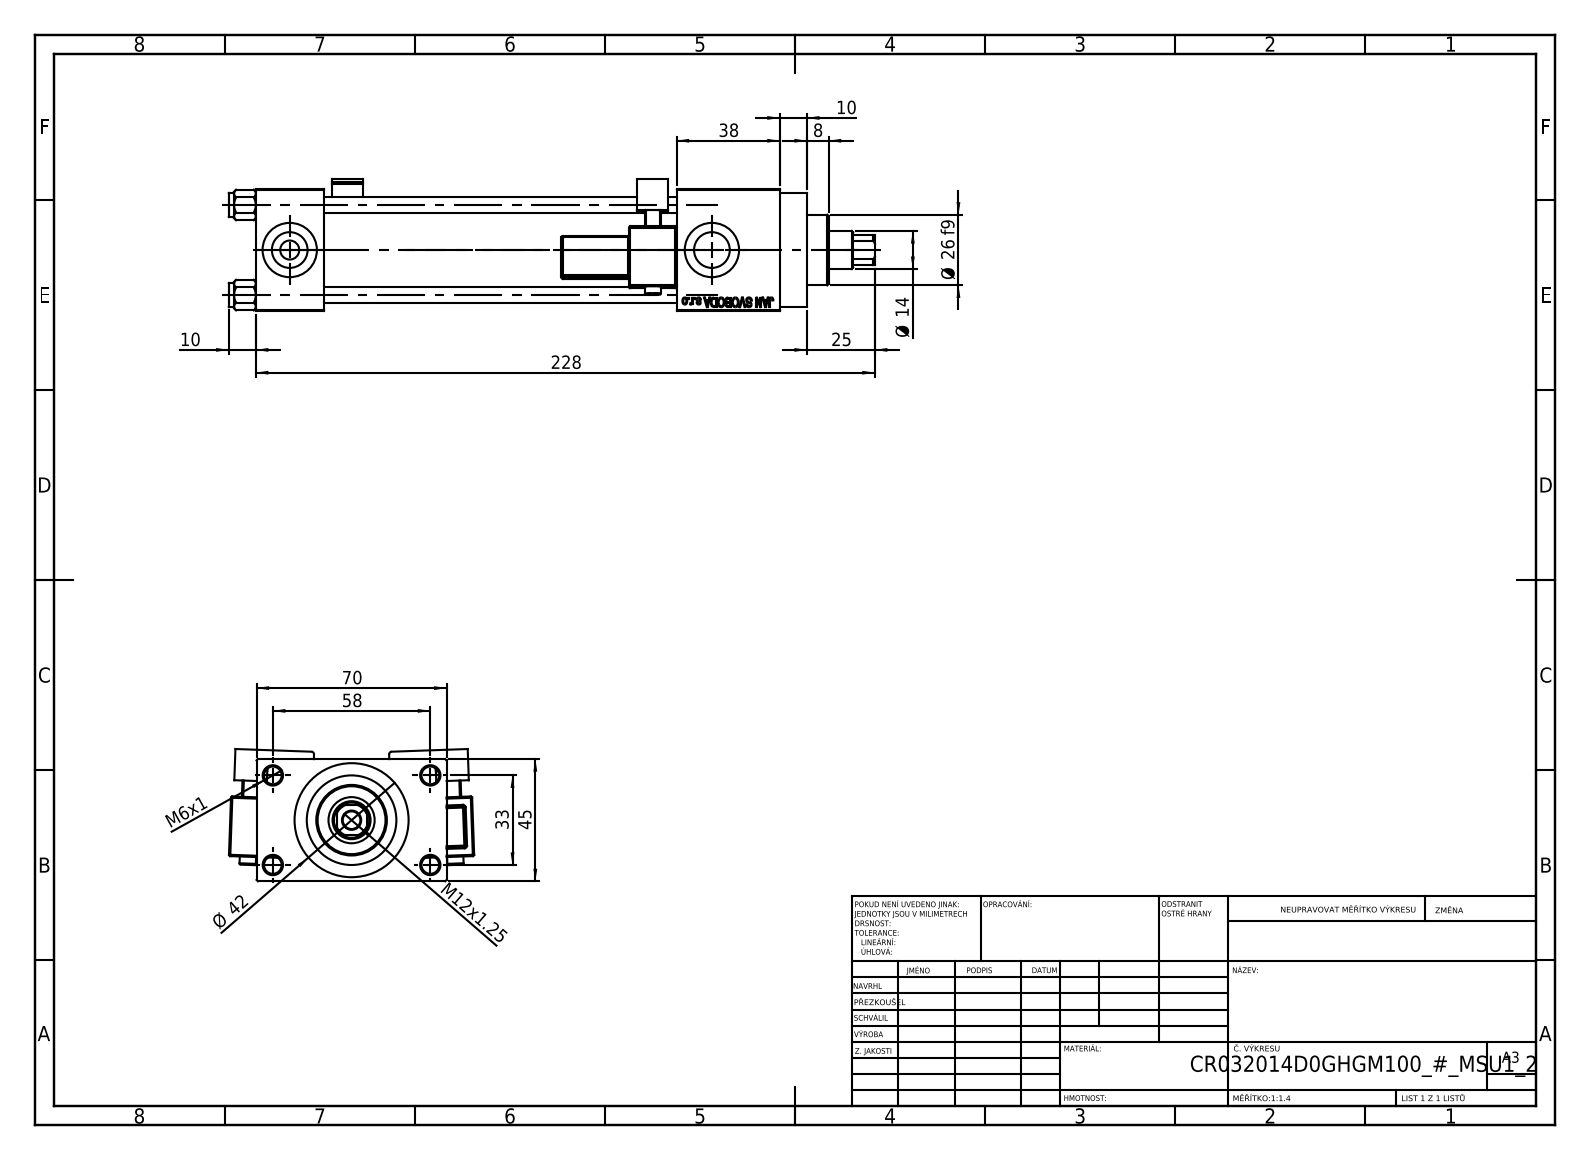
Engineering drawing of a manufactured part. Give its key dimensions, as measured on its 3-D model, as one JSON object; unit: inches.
{"part_name": "V215CR_VCP_D; V215CR_MSU; V215CR_D_TYCINKA; NUT_M5_D (+2 more)", "step_written_by": "SolidWorks 2019 (CONFIG_CONTROL_DESIGN)", "units": "inches", "bodies": {"solids": 13, "faces": 1260, "planar": 558, "cylindrical": 148, "other": 554}, "overall_size": [9.37, 3.556, 1.918], "volume_in3": 19.45, "surface_area_in2": 177.5, "round_holes": [[0.256, 5], [0.236, 4], [0.276, 2], [0.518, 2], [0.787, 2], [0.551, 1], [0.669, 1], [0.945, 1], [1.26, 1], [1.299, 1]], "round_bosses_or_shafts": [[0.354, 4], [0.236, 2], [1.654, 1], [1.496, 1], [1.024, 1]], "partial_cylinders_radius": [[0.02, 48], [0.039, 2], [0.098, 2], [0.157, 2], [0.256, 1]], "face_to_face_distances": [1.772, 0.984, 5.118, 0.492, 0.118, 2.264, 6.102, 6.614, 2.756, 1.496], "hole_center_spacings": [0.488, 0.924, 1.307, 1.314, 1.392, 1.795, 2.219, 1.299]}
